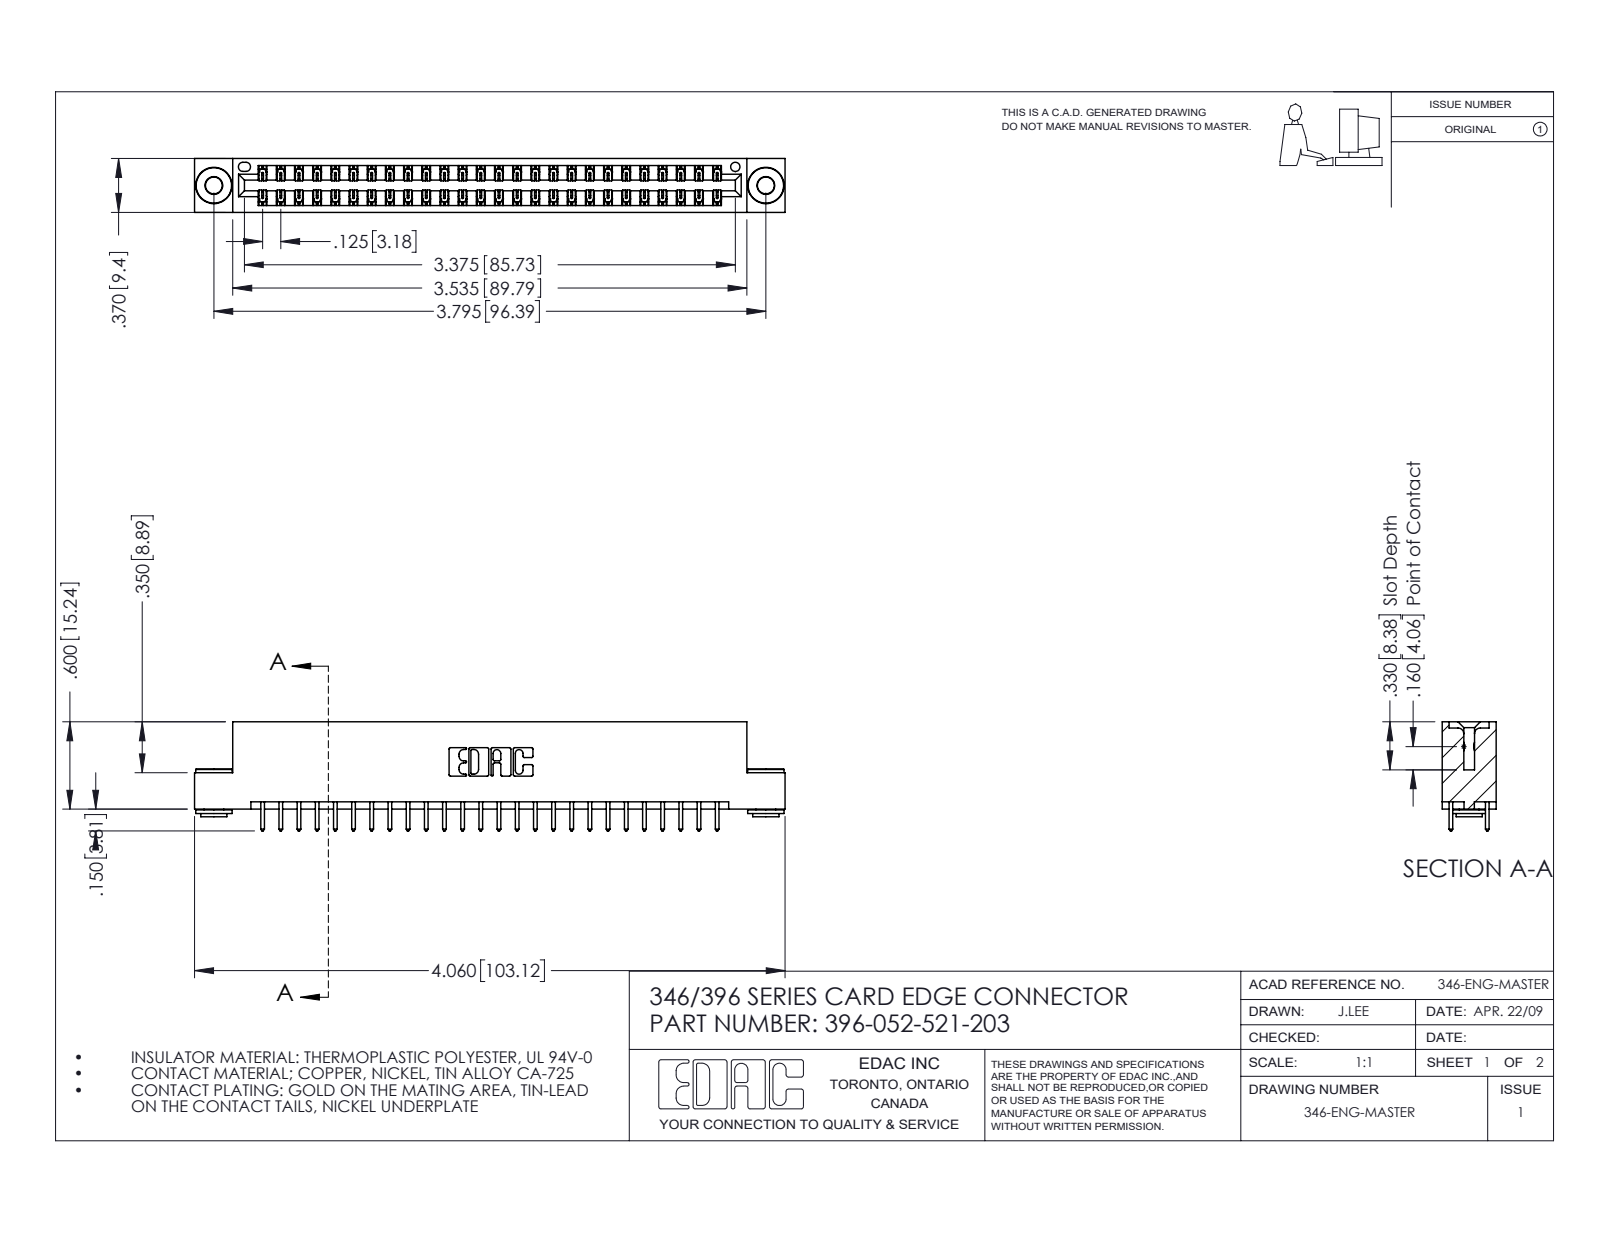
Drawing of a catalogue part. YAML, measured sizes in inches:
part_name: "345-250-002_345-250-002-102; 345-292-001_345-293-121; 396-052-521-203; 346 Part_Flush Mounting Lugs - 0.156 Dia-TH"
step_written_by: "SolidWorks 2016 (CONFIG_CONTROL_DESIGN)"
units: inches
bodies: {solids: 55, faces: 2864, planar: 1906, cylindrical: 950, other: 8}
overall_size: [4.06, 0.75, 0.37]
volume: 0.606
surface_area: 20.88
round_holes:
  - {diameter: 0.116, count: 2}
  - {diameter: 0.156, count: 2}
  - {diameter: 0.064, count: 1}
round_bosses_or_shafts:
  - {diameter: 0.25, count: 2}
  - {diameter: 0.18, count: 2}
  - {diameter: 0.136, count: 2}
partial_cylinders:
  - {radius: 0.006, count: 78}
  - {radius: 0.01, count: 52}
  - {radius: 0.01, count: 22}
  - {radius: 0.007, count: 6}
  - {radius: 0.031, count: 6}
  - {radius: 0.026, count: 3}
  - {radius: 0.014, count: 2}
  - {radius: 0.022, count: 2}
face_to_face_distances: [0.048, 0.322, 0.25, 0.37, 0.025, 0.072, 0.298, 0.275, 0.148, 0.222]
hole_center_spacings: [0.246, 3.587, 3.795]
